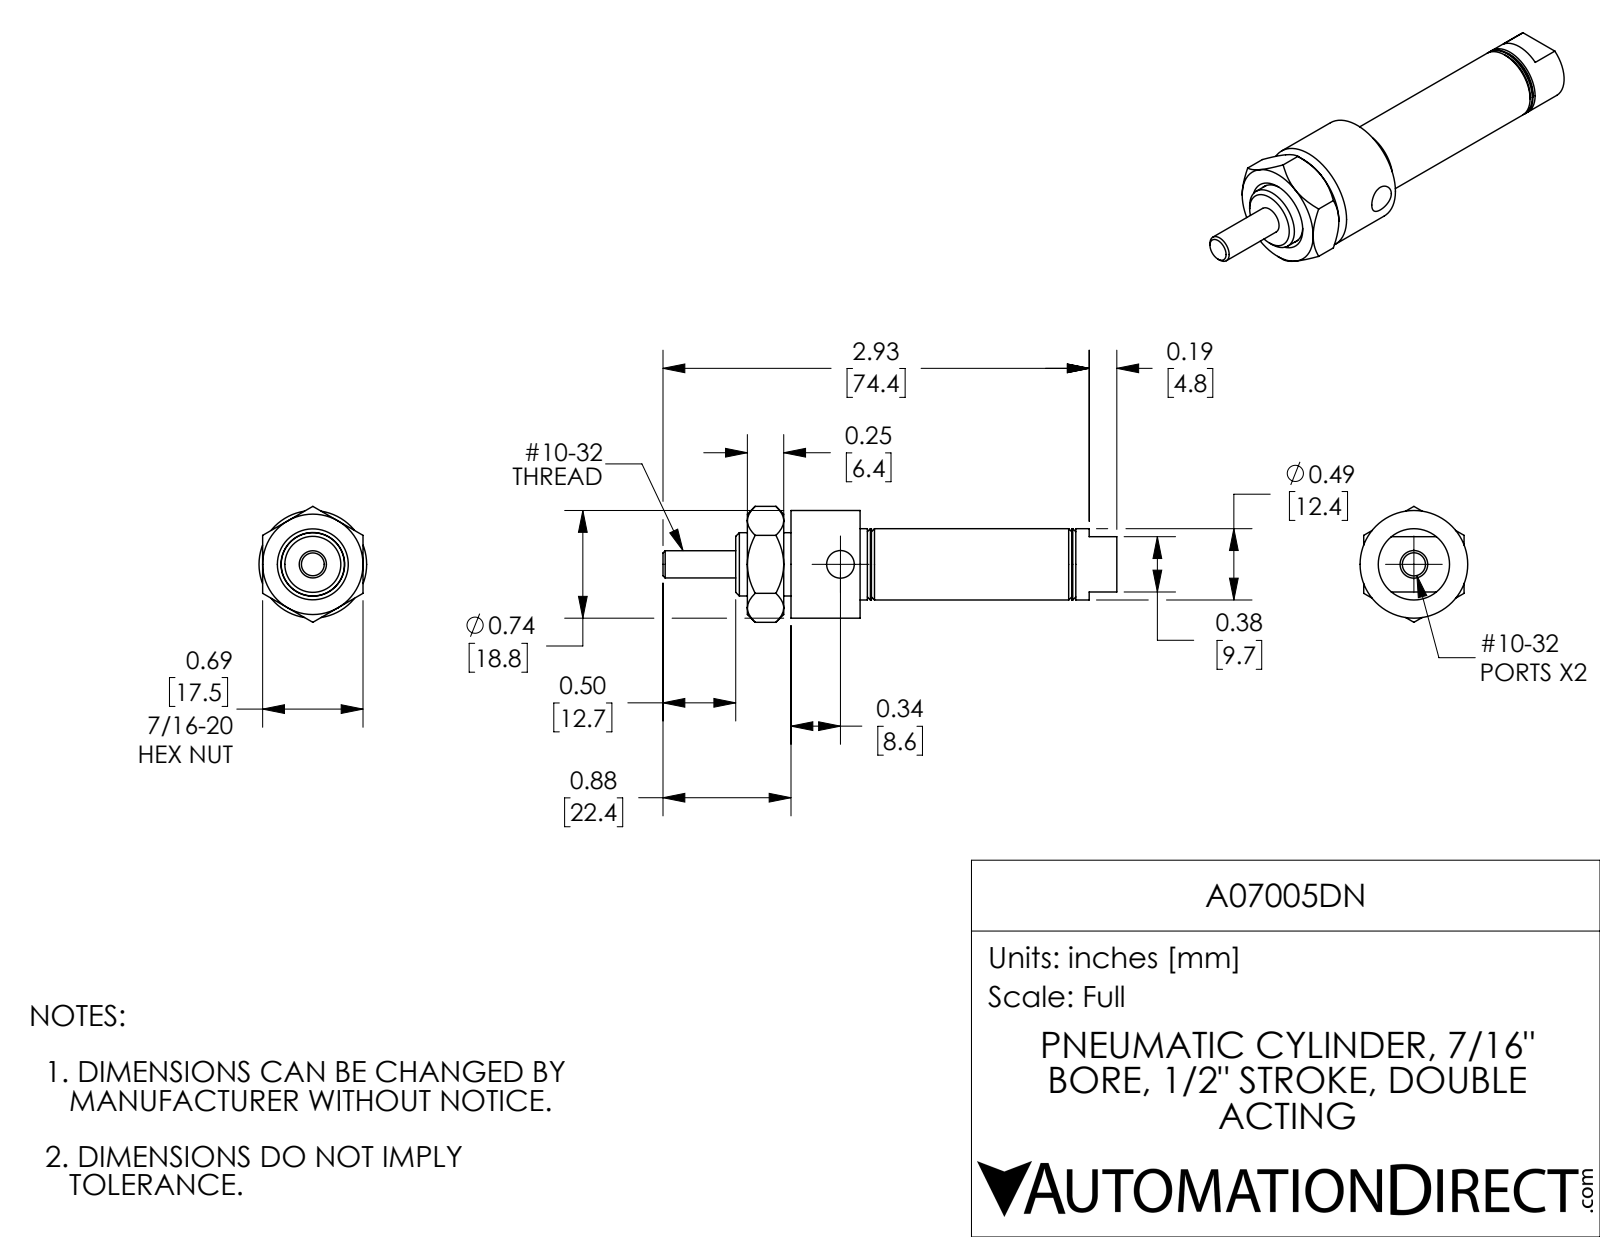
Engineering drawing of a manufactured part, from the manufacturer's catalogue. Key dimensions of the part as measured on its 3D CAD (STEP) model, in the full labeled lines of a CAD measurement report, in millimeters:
Part name (STEP PRODUCT): A07005DN-MainBody; A07005DN_Mounting Nut_D-154; A07005DN-Rod; A07005DN
STEP written by: SolidWorks 2017 (AUTOMOTIVE_DESIGN)
Units: millimetres
Bodies: 3 solids, 92 faces (28 planar, 32 cylindrical, 32 other)
Overall size (bounding box): 79.2 × 20.2 × 18.8
Volume: 9 490 mm³ · Surface area: 7 452 mm²
Round holes (diameter × count): ⌀4 ×2, ⌀4.8 ×2, ⌀4.7 ×1, ⌀11.1 ×1
Round bosses / shafts (diameter × count): ⌀18.8 ×1, ⌀12.4 ×1, ⌀11 ×1
Main face-to-face distances: 41.1, 12.7, 15.7, 17.5, 28.4, 29.1, 12.1, 1.3, 13.3, 25.4
